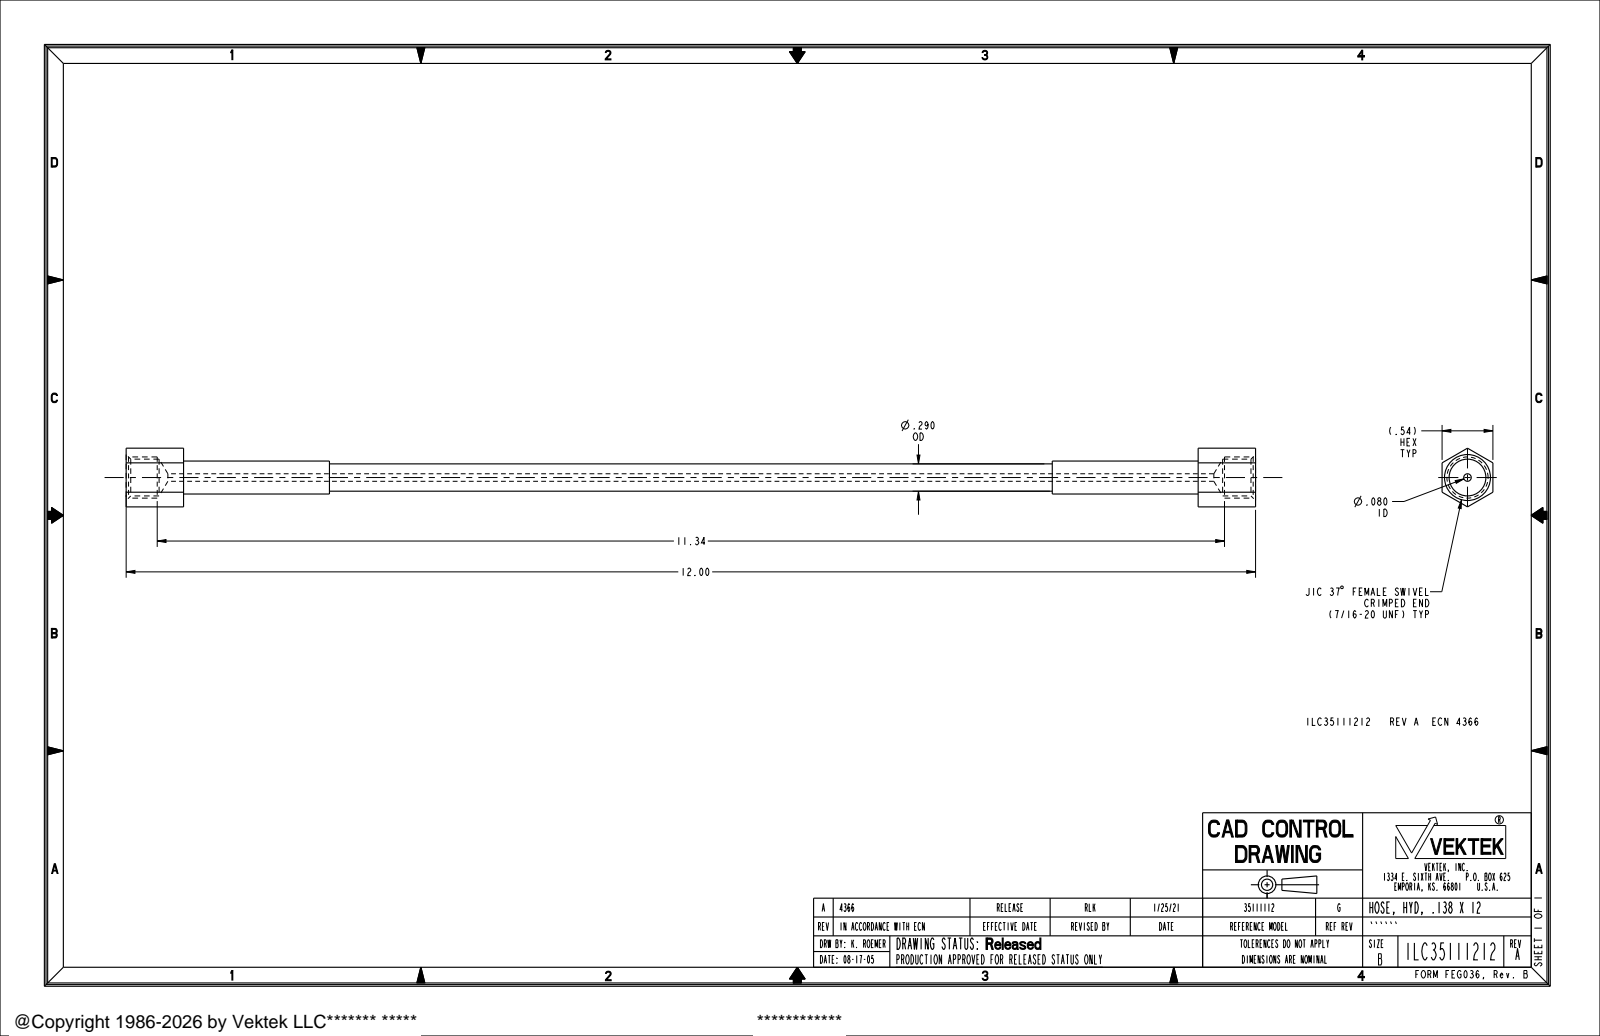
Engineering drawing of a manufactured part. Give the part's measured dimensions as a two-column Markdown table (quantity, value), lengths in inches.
| quantity | value |
| --- | --- |
| part name | ILC35111212 |
| STEP written by | PRO/ENGINEER BY PARAMETRIC TECHNOLOGY CORPORATION, 2017170 (AUTOMOTIVE_DESIGN) |
| units | inches |
| bodies | 1 solid, 44 faces (20 planar, 16 cylindrical, 8 other) |
| overall size | 12 × 0.624 × 0.54 |
| volume | 0.961 in³ |
| surface area | 18.08 in² |
| round holes (diameter × count) | 0.08 × 1, 0.391 × 1, 0.437 × 1 |
| round bosses / shafts (diameter × count) | 0.35 × 1, 0.29 × 1 |
| main face-to-face distances | 0.54, 10.78, 0.61, 11.39, 12, 0.33, 11.67, 0.28, 11.06, 2.16 |
